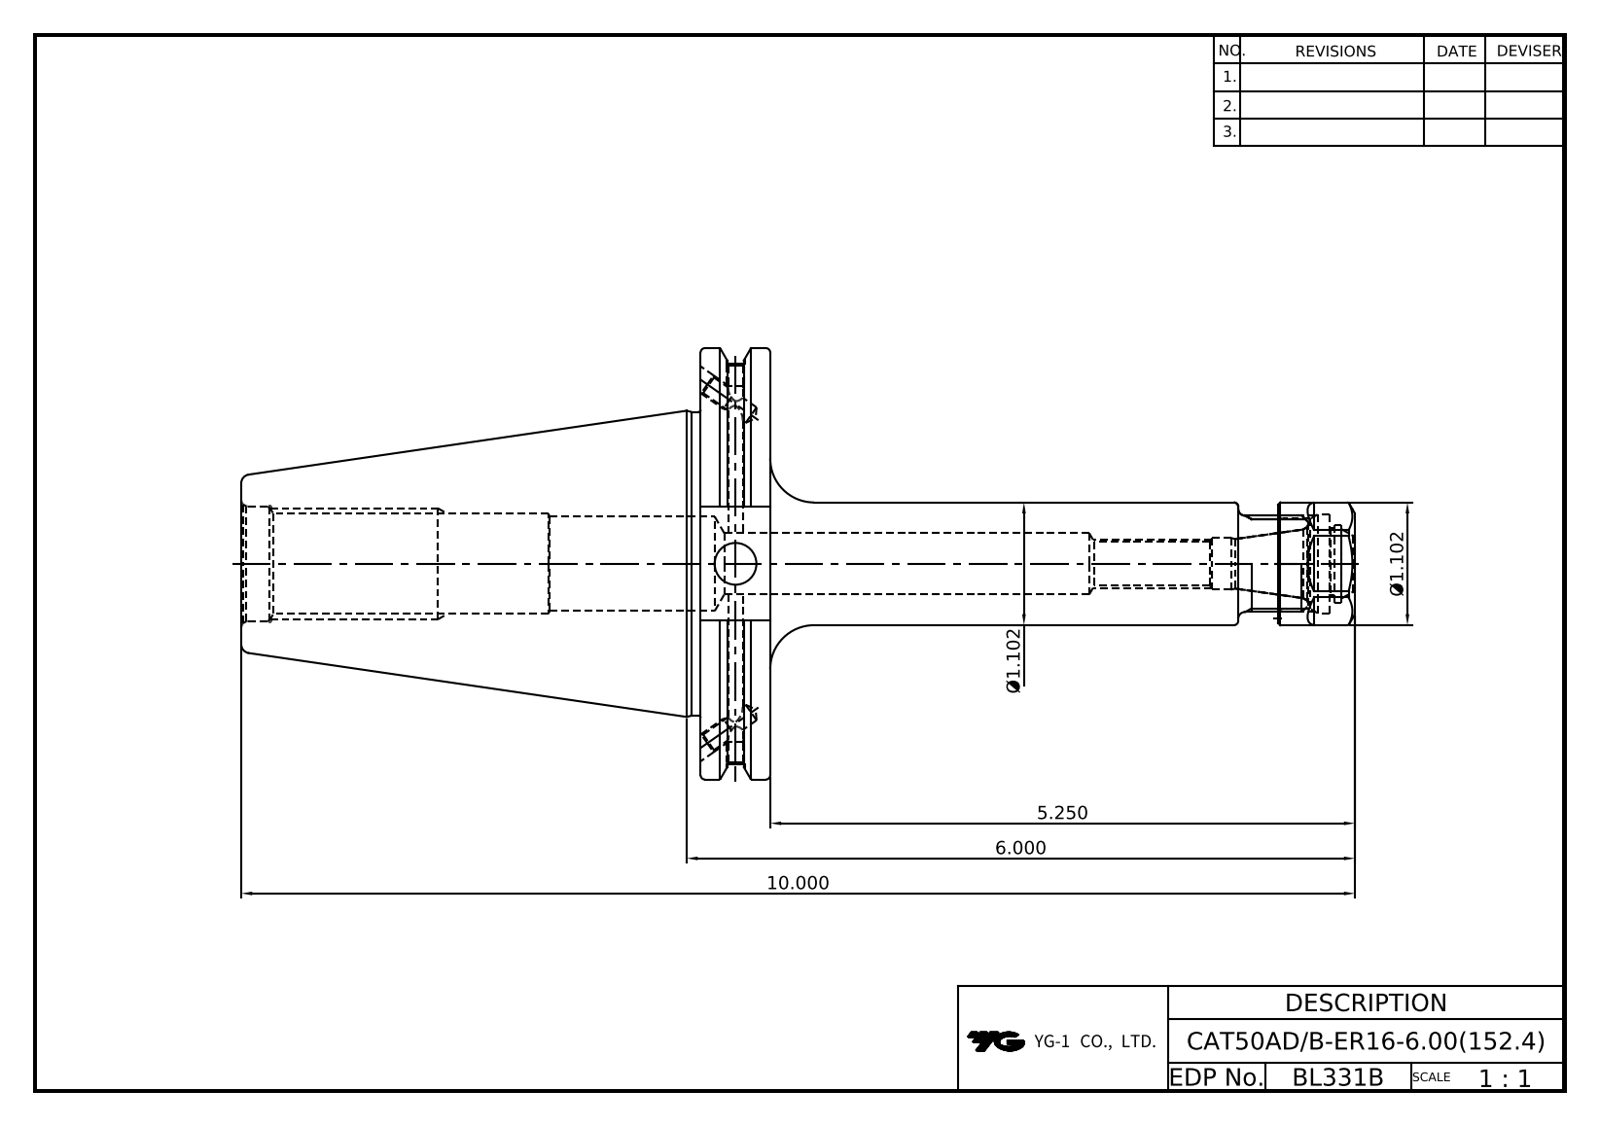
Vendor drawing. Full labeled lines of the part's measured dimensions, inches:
Part name (STEP PRODUCT): BL331B-CAT50ADB-ER16-6_0; ER16NUT_3D_20140325; BL331B-CAT50ADB-ER16-6_0_ASM
STEP written by: PRO/ENGINEER BY PARAMETRIC TECHNOLOGY CORPORATION, 2012130 (CONFIG_CONTROL_DESIGN)
Units: inches
Bodies: 2 solids, 200 faces (60 planar, 76 cylindrical, 64 other)
Overall size (bounding box): 10 × 3.874 × 3.717
Volume: 23.49 in³ · Surface area: 100.5 in²
Round holes (diameter × count): ⌀0.197 ×5, ⌀0.165 ×3, ⌀0.039 ×1, ⌀0.394 ×1, ⌀0.394 ×1, ⌀0.464 ×1, ⌀0.504 ×1, ⌀0.551 ×1, ⌀0.697 ×1, ⌀0.811 ×1, ⌀0.846 ×1, ⌀0.886 ×1
Round bosses / shafts (diameter × count): ⌀3.874 ×1, ⌀3.594 ×1, ⌀2.726 ×1, ⌀1.102 ×1, ⌀1.102 ×1, ⌀0.866 ×1, ⌀0.866 ×1
Partial cylindrical surfaces — rounded edges, fillets, slot ends (radius × count): R0.303 ×2
Main face-to-face distances: 0.625, 4.125, 4.75, 2.882, 0.984, 10, 5.875, 5.25, 1.012, 0.014
Hole centre spacings: 0.472
